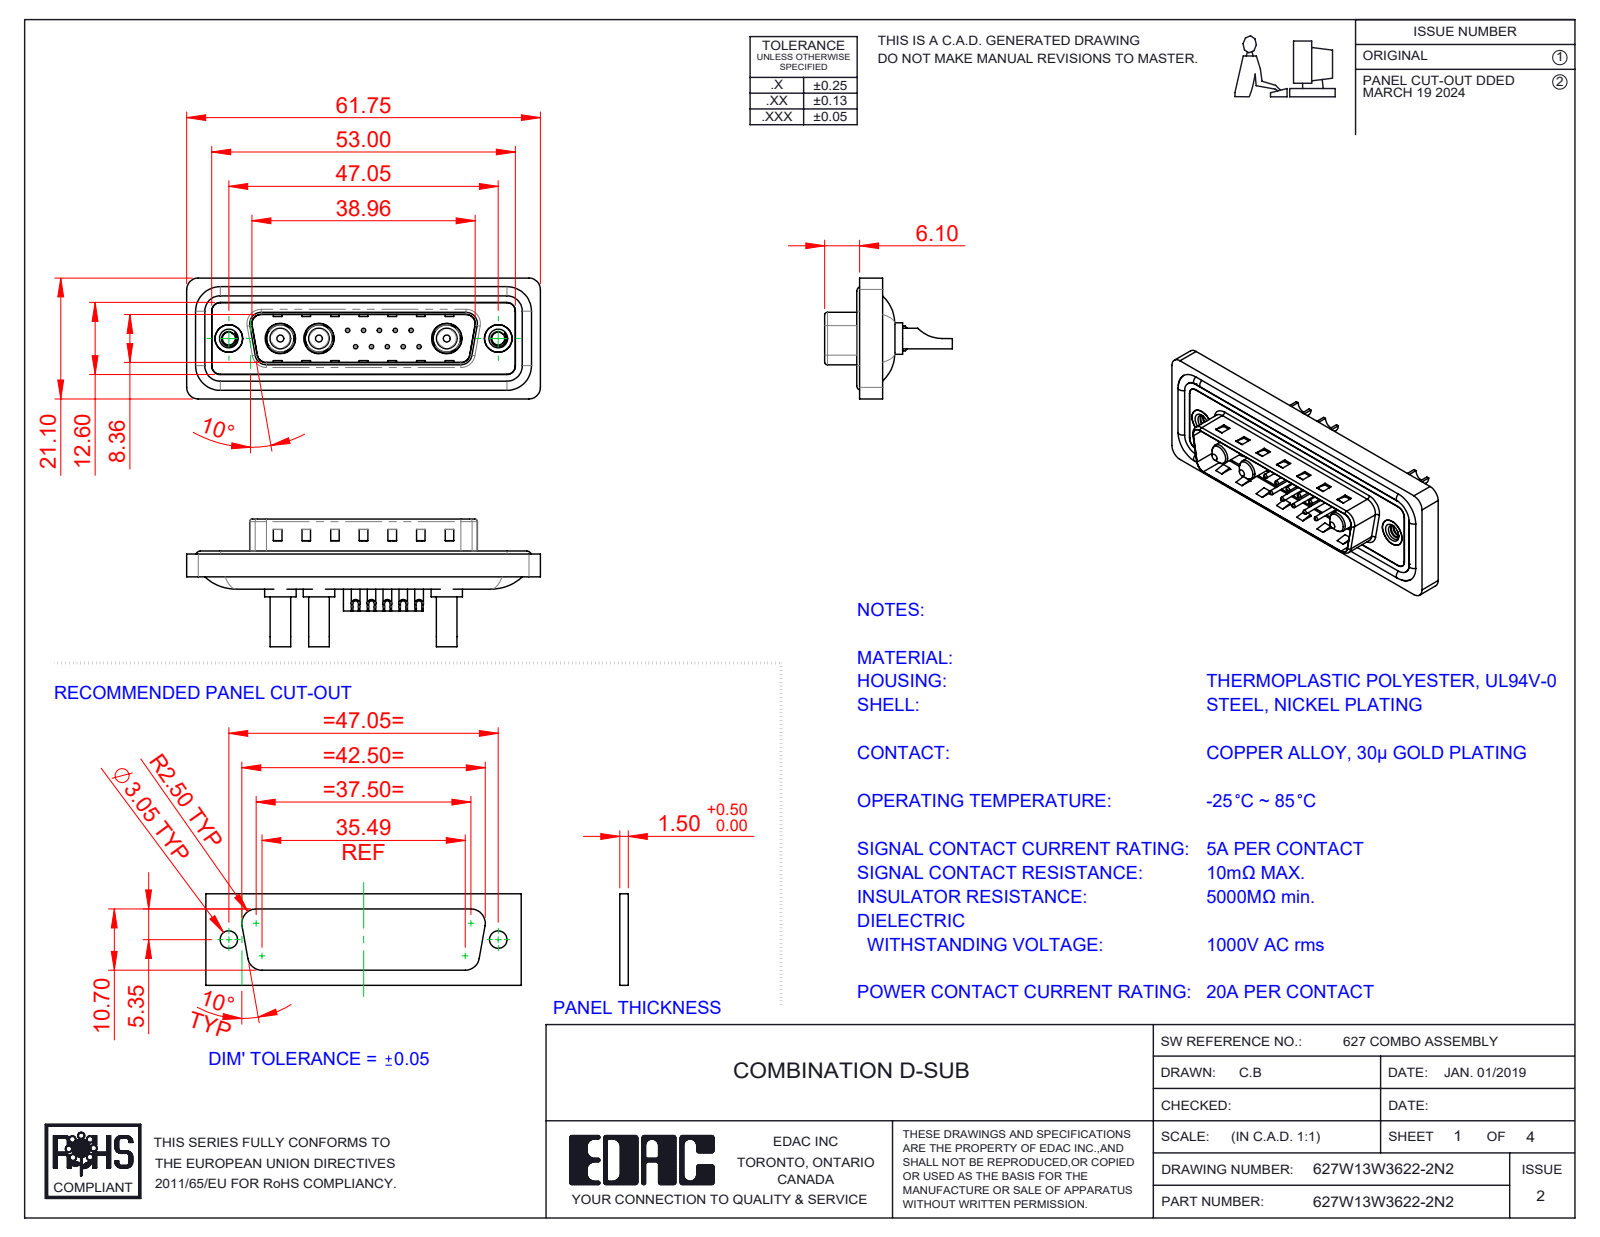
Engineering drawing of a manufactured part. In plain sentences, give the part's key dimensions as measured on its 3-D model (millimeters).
The part is named "627W13W3622-2N2; Power Pin_20A SC; 627Combo Shell Front_25 Contacts; 627Combo Contact Row 1_22 (+5 more)". Its 3-D file was written by "SolidWorks 2023 (CONFIG_CONTROL_DESIGN)". It is 23 solids with 991 faces: 338 planar, 414 cylindrical and 239 other. Overall it measures 61.75 by 22.3 by 21.1 millimeters. Its volume is 7 389 cubic millimeters and its surface area 12 202 square millimeters. Round holes: 10 of diameter 0.75, 10 of diameter 1, 10 of diameter 1.6, 10 of diameter 2, 3 of diameter 2.7, 3 of diameter 4.85, 3 of diameter 5.3, 2 of diameter 2.26, 2 of diameter 4, 2 of diameter 4.8, 2 of diameter 5. Round bosses or shafts: 10 of diameter 1.5, 4 of diameter 1.6, 3 of diameter 5.5, 3 of diameter 5.2, 3 of diameter 4.75, 3 of diameter 3.75, 3 of diameter 3.6, 2 of diameter 4.9. Partial cylindrical surfaces (rounded edges, fillets, slot ends): 22 of radius 1.5, 18 of radius 2, 8 of radius 0.5, 8 of radius 1.6, 6 of radius 1, 4 of radius 0.25, 4 of radius 0.6, 4 of radius 0.65. The main face-to-face distances are 0.4, 1.5, 1.1, 1.6, 0.5, 3.1, 2.9, 0.82, 9.58, 4.1. The hole center spacings are 3.16, 2.77, 5.04, 5.54, 7.49, 5.03, 8.31, 10.11.
